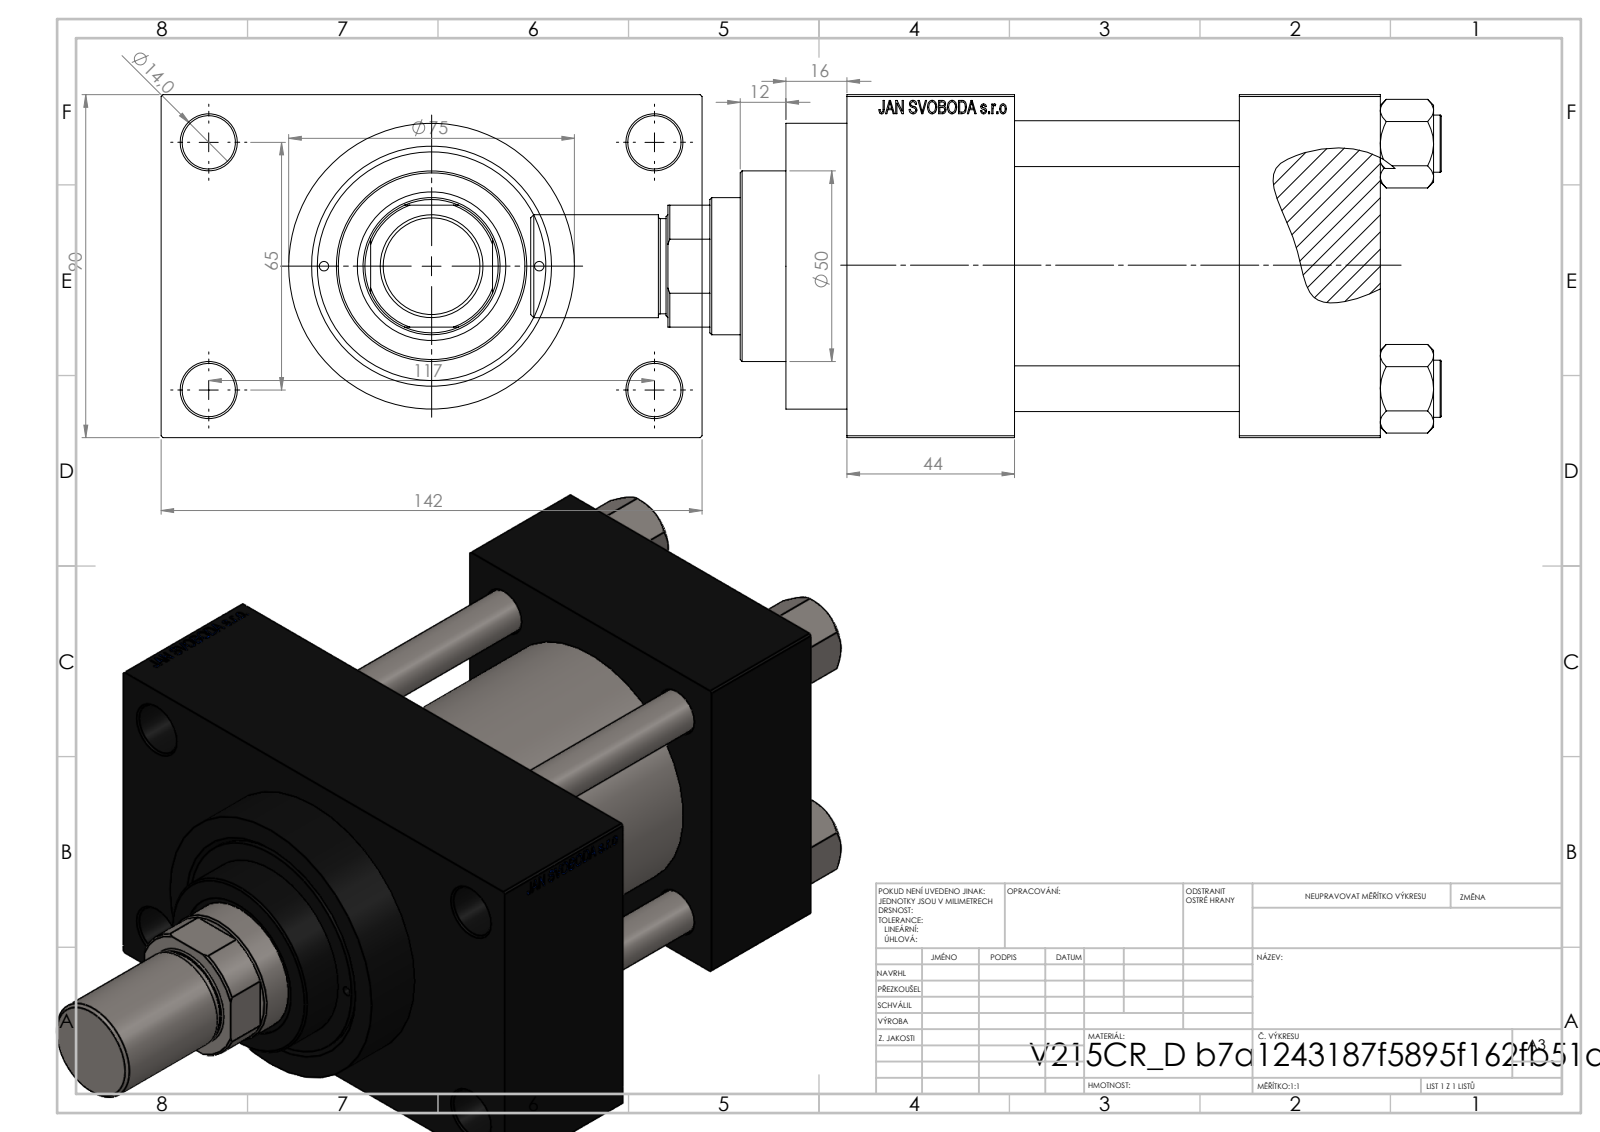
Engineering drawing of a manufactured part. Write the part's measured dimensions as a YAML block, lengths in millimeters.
part_name: "V215_VC_A; V215CR_VCP_D; ROD_END_AH; NUT_M5_D (+2 more)"
step_written_by: "SolidWorks 2019 (CONFIG_CONTROL_DESIGN)"
units: millimeters
bodies: {solids: 12, faces: 1125, planar: 503, cylindrical: 96, other: 526}
overall_size: [239, 142, 90]
volume: 1132000
surface_area: 209967
round_holes:
  - {diameter: 12, count: 4}
  - {diameter: 14, count: 4}
  - {diameter: 2.5, count: 2}
  - {diameter: 7, count: 2}
  - {diameter: 20.96, count: 2}
  - {diameter: 30, count: 2}
  - {diameter: 25.5, count: 1}
  - {diameter: 36, count: 1}
  - {diameter: 39, count: 1}
  - {diameter: 50, count: 1}
  - {diameter: 60, count: 1}
  - {diameter: 63, count: 1}
round_bosses_or_shafts:
  - {diameter: 15, count: 4}
  - {diameter: 75, count: 1}
  - {diameter: 69, count: 1}
  - {diameter: 27, count: 1}
  - {diameter: 25, count: 1}
partial_cylinders:
  - {radius: 17.5, count: 1}
face_to_face_distances: [90, 59, 37, 96, 140, 103, 44, 26, 116, 142]
hole_center_spacings: [26.35, 32.39, 44.4, 45.47, 64.3, 66.92, 68.42, 69.81]
